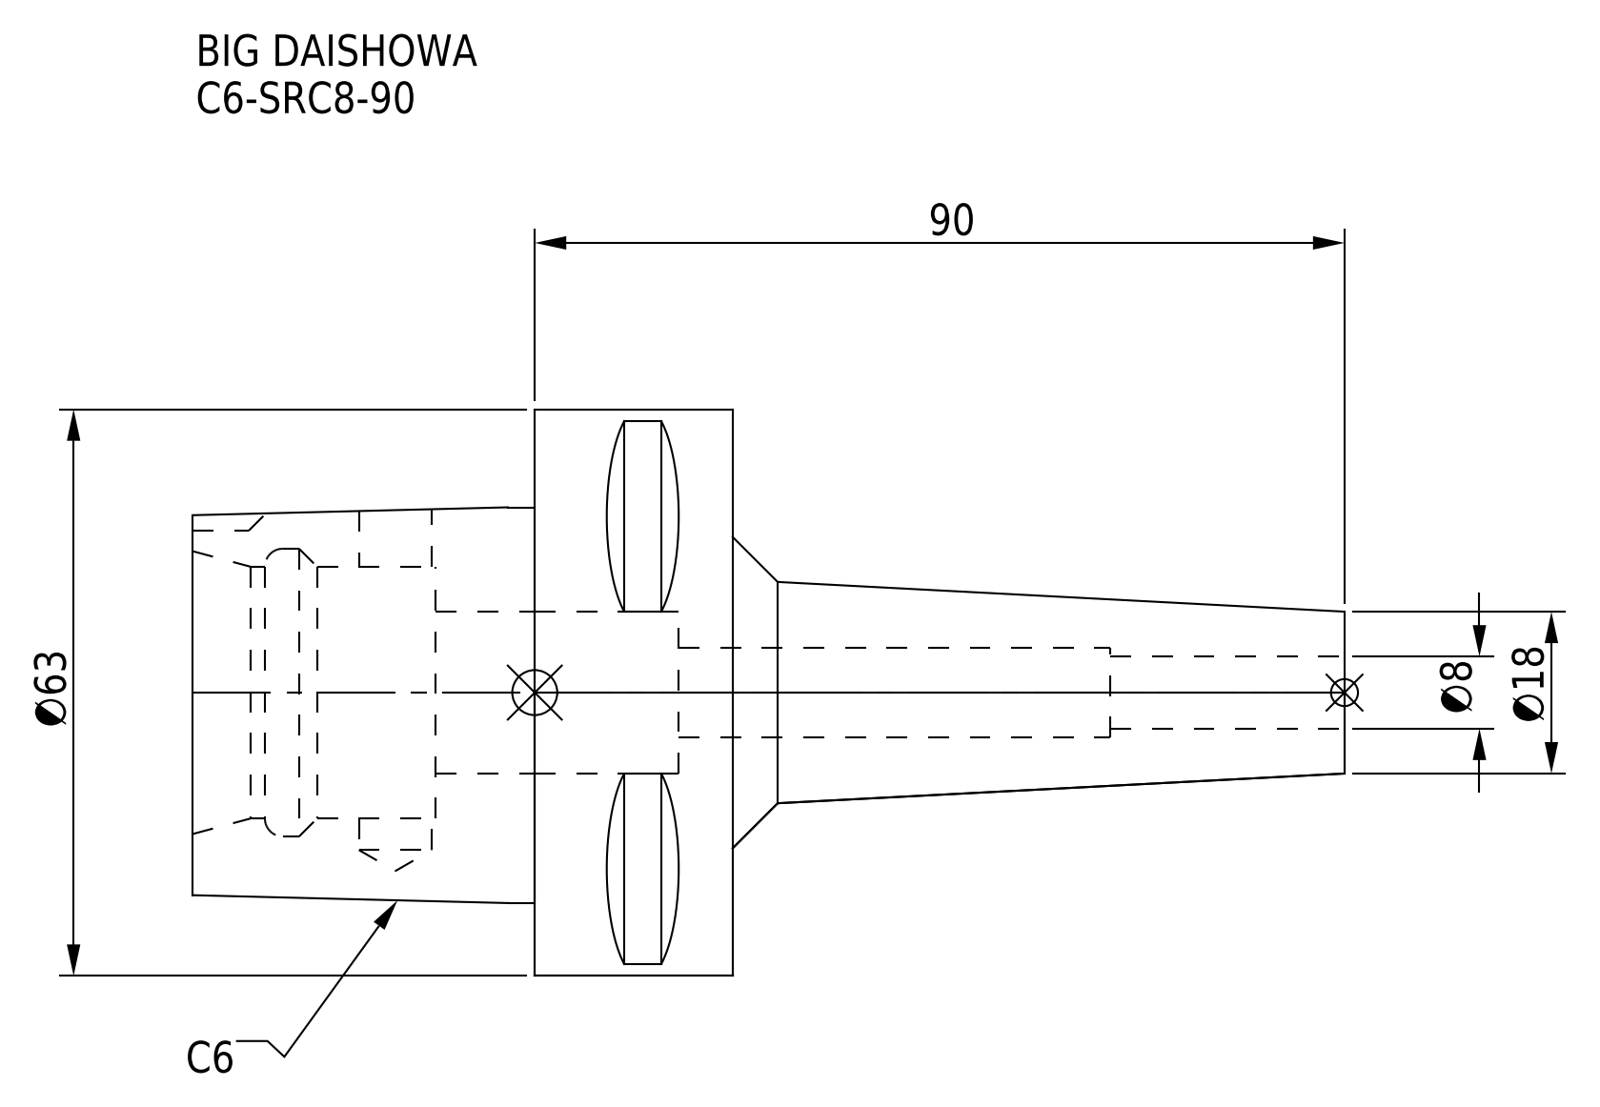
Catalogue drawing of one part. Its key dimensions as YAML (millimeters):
part_name: "C6-SRC8-90"
step_written_by: "CREO PARAMETRIC BY PTC INC, 2016380 (AUTOMOTIVE_DESIGN)"
units: millimeters
bodies: {solids: 1, faces: 62, planar: 29, cylindrical: 19, other: 14}
overall_size: [128, 63, 63]
volume: 117615
surface_area: 26404
round_holes:
  - {diameter: 8, count: 1}
  - {diameter: 8.1, count: 1}
  - {diameter: 10, count: 1}
  - {diameter: 18, count: 1}
  - {diameter: 28, count: 1}
  - {diameter: 32, count: 1}
round_bosses_or_shafts:
  - {diameter: 63, count: 1}
partial_cylinders:
  - {radius: 5, count: 1}
face_to_face_distances: [22, 27, 60, 38, 33, 11, 24.89, 55.4, 68, 90]
